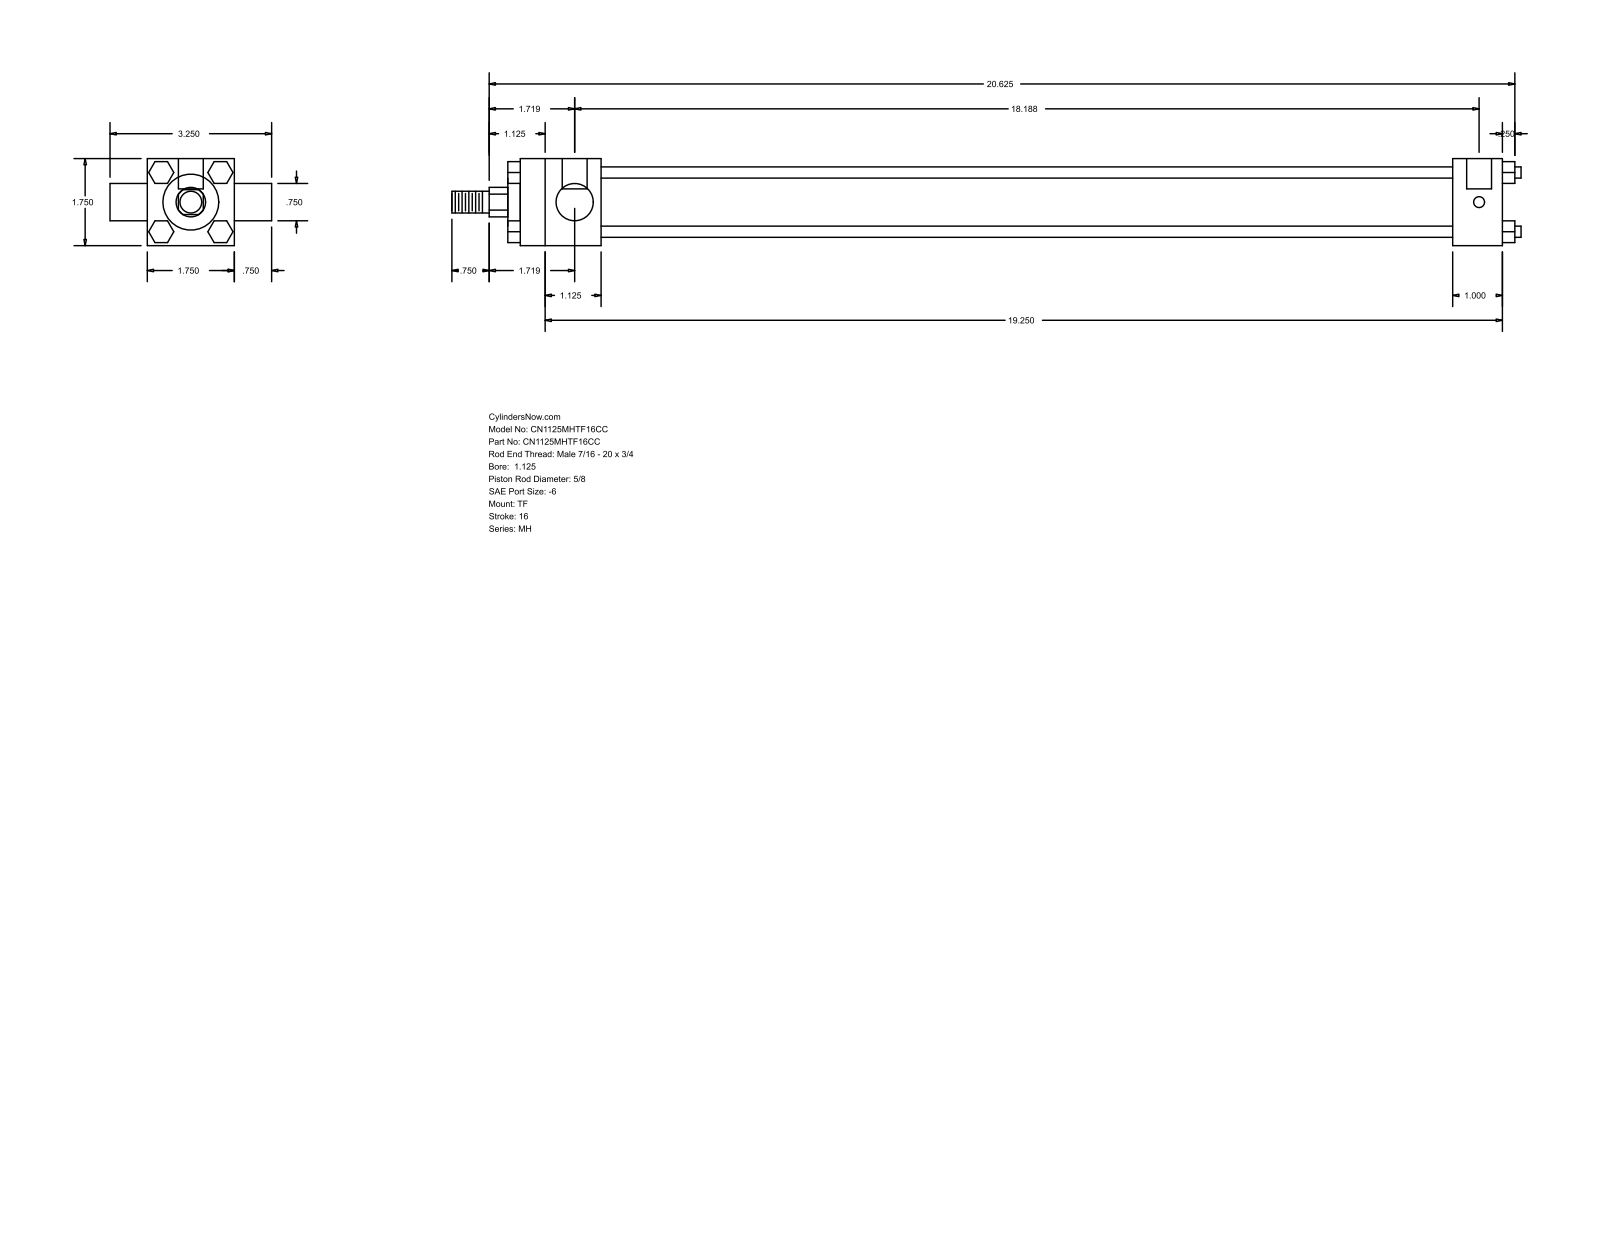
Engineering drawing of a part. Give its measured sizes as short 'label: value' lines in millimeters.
name: MH_TF__0112_0.625
written by: GSSL Pune (CONFIG_CONTROL_DESIGN)
unit: mm
bodies: 0 solids, 120 faces (92 planar, 28 cylindrical, 0 other)
size: 546.1 × 82.55 × 44.45
holes: 3× ⌀5.56, 2× ⌀12.7
bosses: 4× ⌀5.71, 1× ⌀34.92, 1× ⌀28.57, 1× ⌀19.05, 1× ⌀15.88, 1× ⌀11.11
rounds: 1× R7.54
face distances: 44.46, 11.11, 25.4, 434.97, 460.37, 41.27, 476.24, 501.64, 47.62, 6.35
hole spacings: 3.17, 458.79, 461.96
